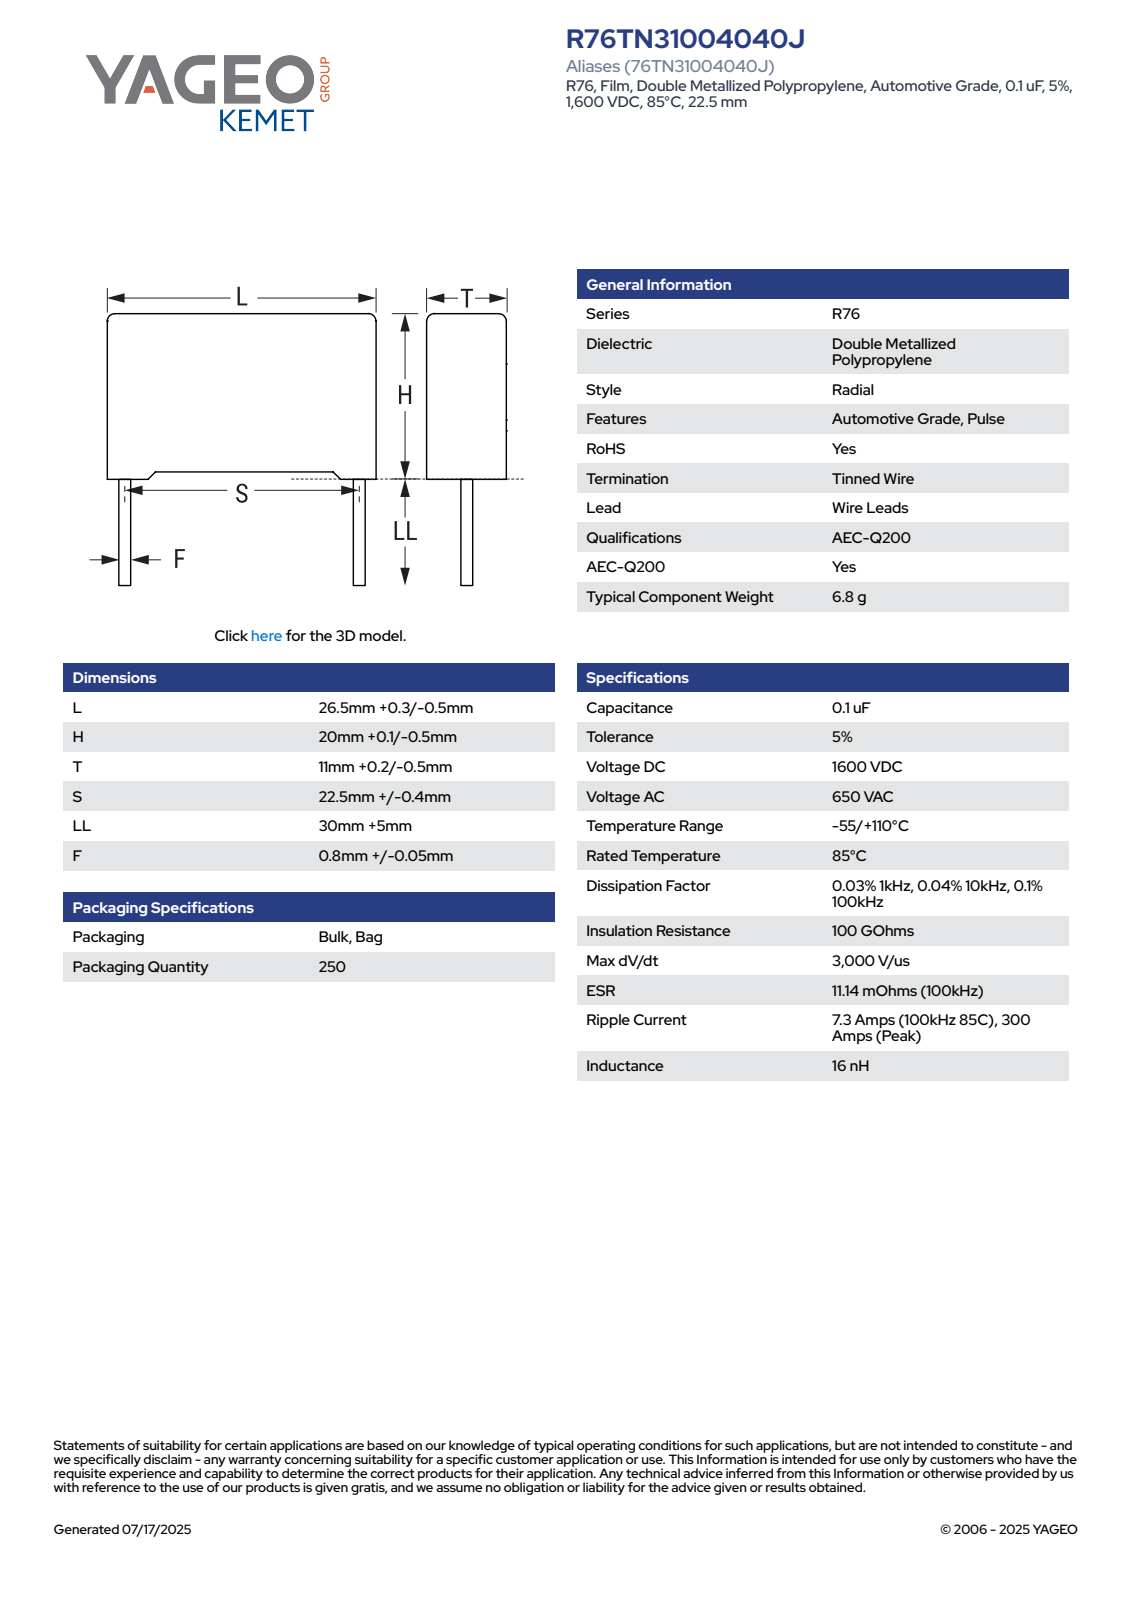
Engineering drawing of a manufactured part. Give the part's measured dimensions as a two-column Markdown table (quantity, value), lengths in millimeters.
| quantity | value |
| --- | --- |
| part name | CFR_RB2_26.5X20X11_L26.8H20.1T11.2S22.5LL35F0.85 |
| STEP written by | SolidWorks 2021 (AUTOMOTIVE_DESIGN) |
| units | millimeters |
| bodies | 4 solids, 85 faces (77 planar, 8 cylindrical, 0 other) |
| overall size | 55.1 × 26.8 × 11.21 |
| volume | 5 870 mm³ |
| surface area | 2 357 mm² |
| round bosses / shafts (diameter × count) | 0.85 × 2 |
| partial cylindrical surfaces (radius × count) | 0.5 × 4 |
| main face-to-face distances | 11.2, 19.35, 26.8, 19.41, 0.75, 0.69, 20.1, 0.89, 25.91, 11.21 |
